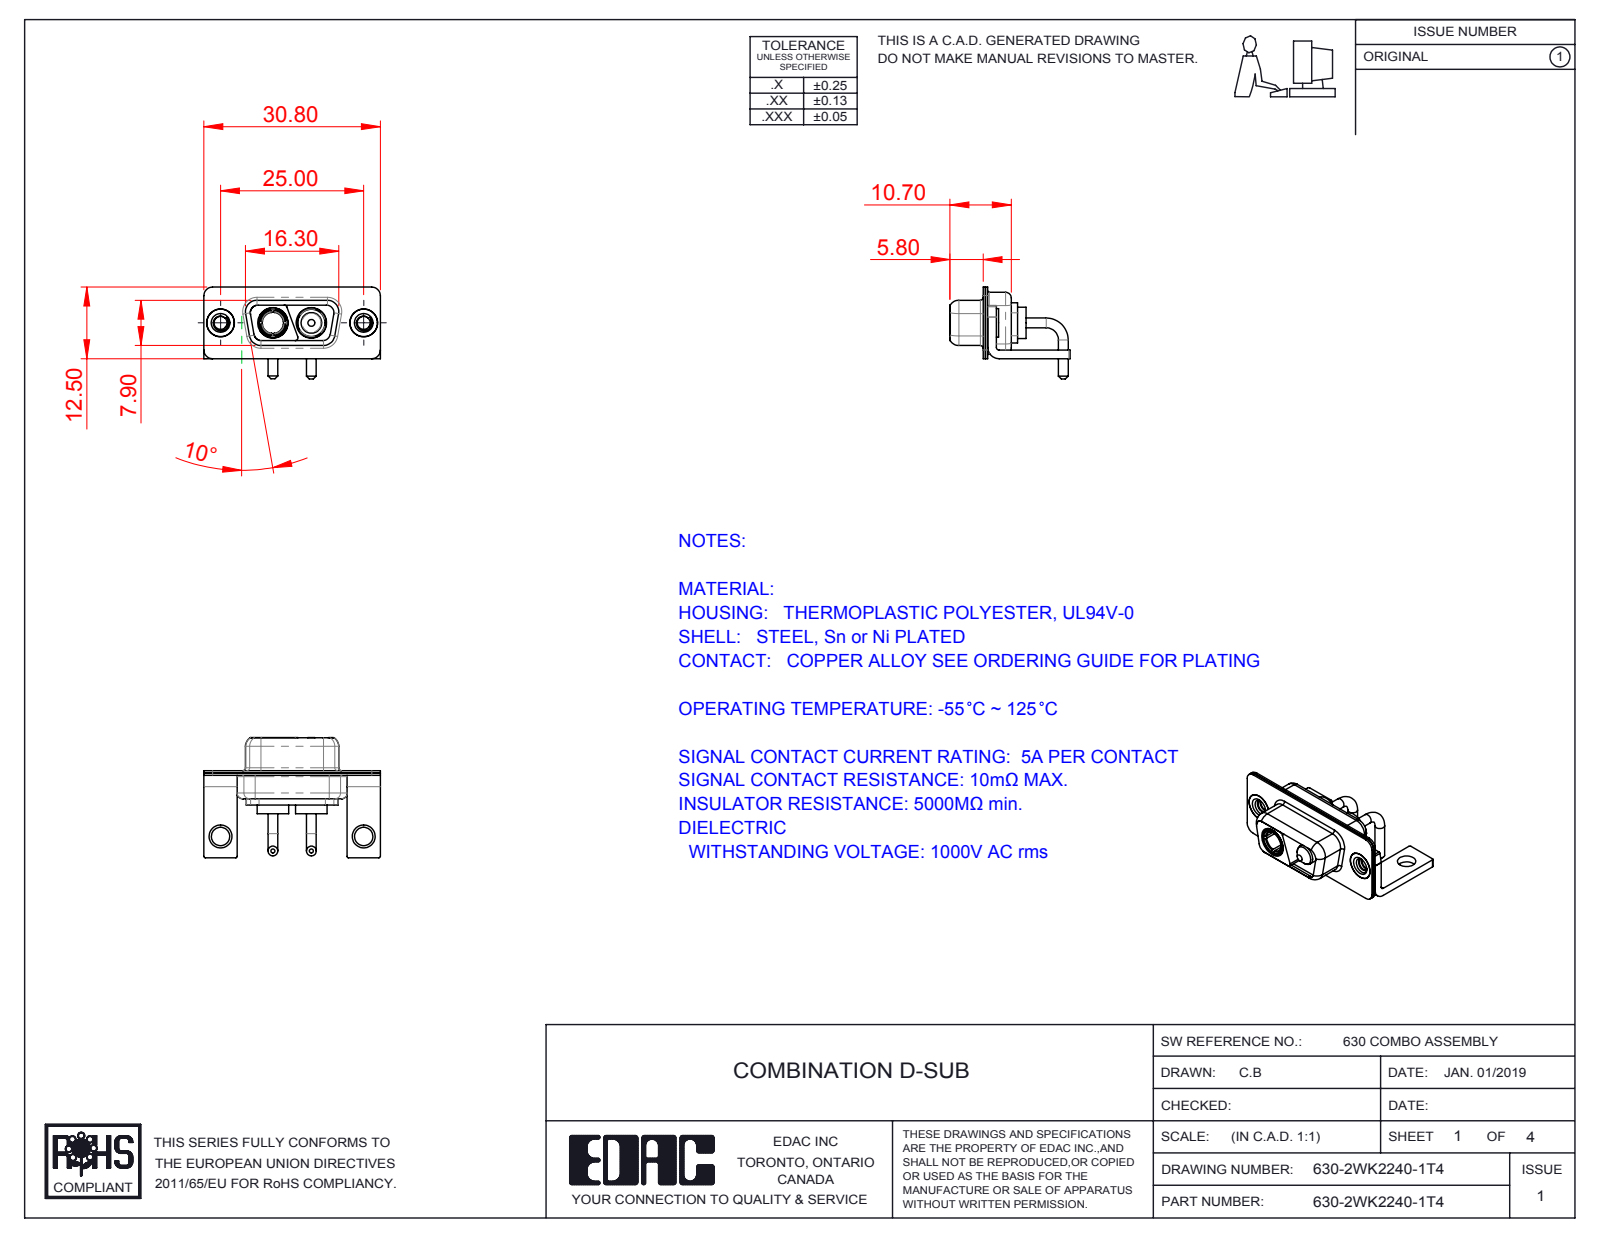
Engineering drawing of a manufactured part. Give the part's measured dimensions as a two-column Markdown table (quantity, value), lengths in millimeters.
| quantity | value |
| --- | --- |
| part name | 630Combo Shell Rear_09 Contacts; Power Socket_10A RA; Power Pin_10A RA; 630-2WK2240-1T4 (+4 more) |
| STEP written by | SolidWorks 2020 (CONFIG_CONTROL_DESIGN) |
| units | millimeters |
| bodies | 11 solids, 441 faces (126 planar, 202 cylindrical, 113 other) |
| overall size | 30.8 × 21 × 16.05 |
| volume | 1 849 mm³ |
| surface area | 4 587 mm² |
| round holes (diameter × count) | 4.85 × 4, 2.26 × 2, 3.2 × 2, 4 × 2, 4.05 × 2, 5.3 × 2, 3.7 × 1 |
| round bosses / shafts (diameter × count) | 1.7 × 4, 5.5 × 2, 5.2 × 2, 5 × 2, 4.95 × 2, 4.8 × 2, 4.75 × 2, 3.75 × 2 |
| partial cylindrical surfaces (radius × count) | 0.25 × 16, 1.5 × 16, 2 × 13, 1.35 × 8, 1.6 × 8, 0.5 × 7, 0.6 × 4, 0.65 × 4 |
| main face-to-face distances | 0.4, 1.5, 0.8, 1.4, 8.45, 0.45, 1.8, 2.3, 8.9, 3.7 |
| hole center spacings | 9.14, 15.86, 25, 6.72 |
